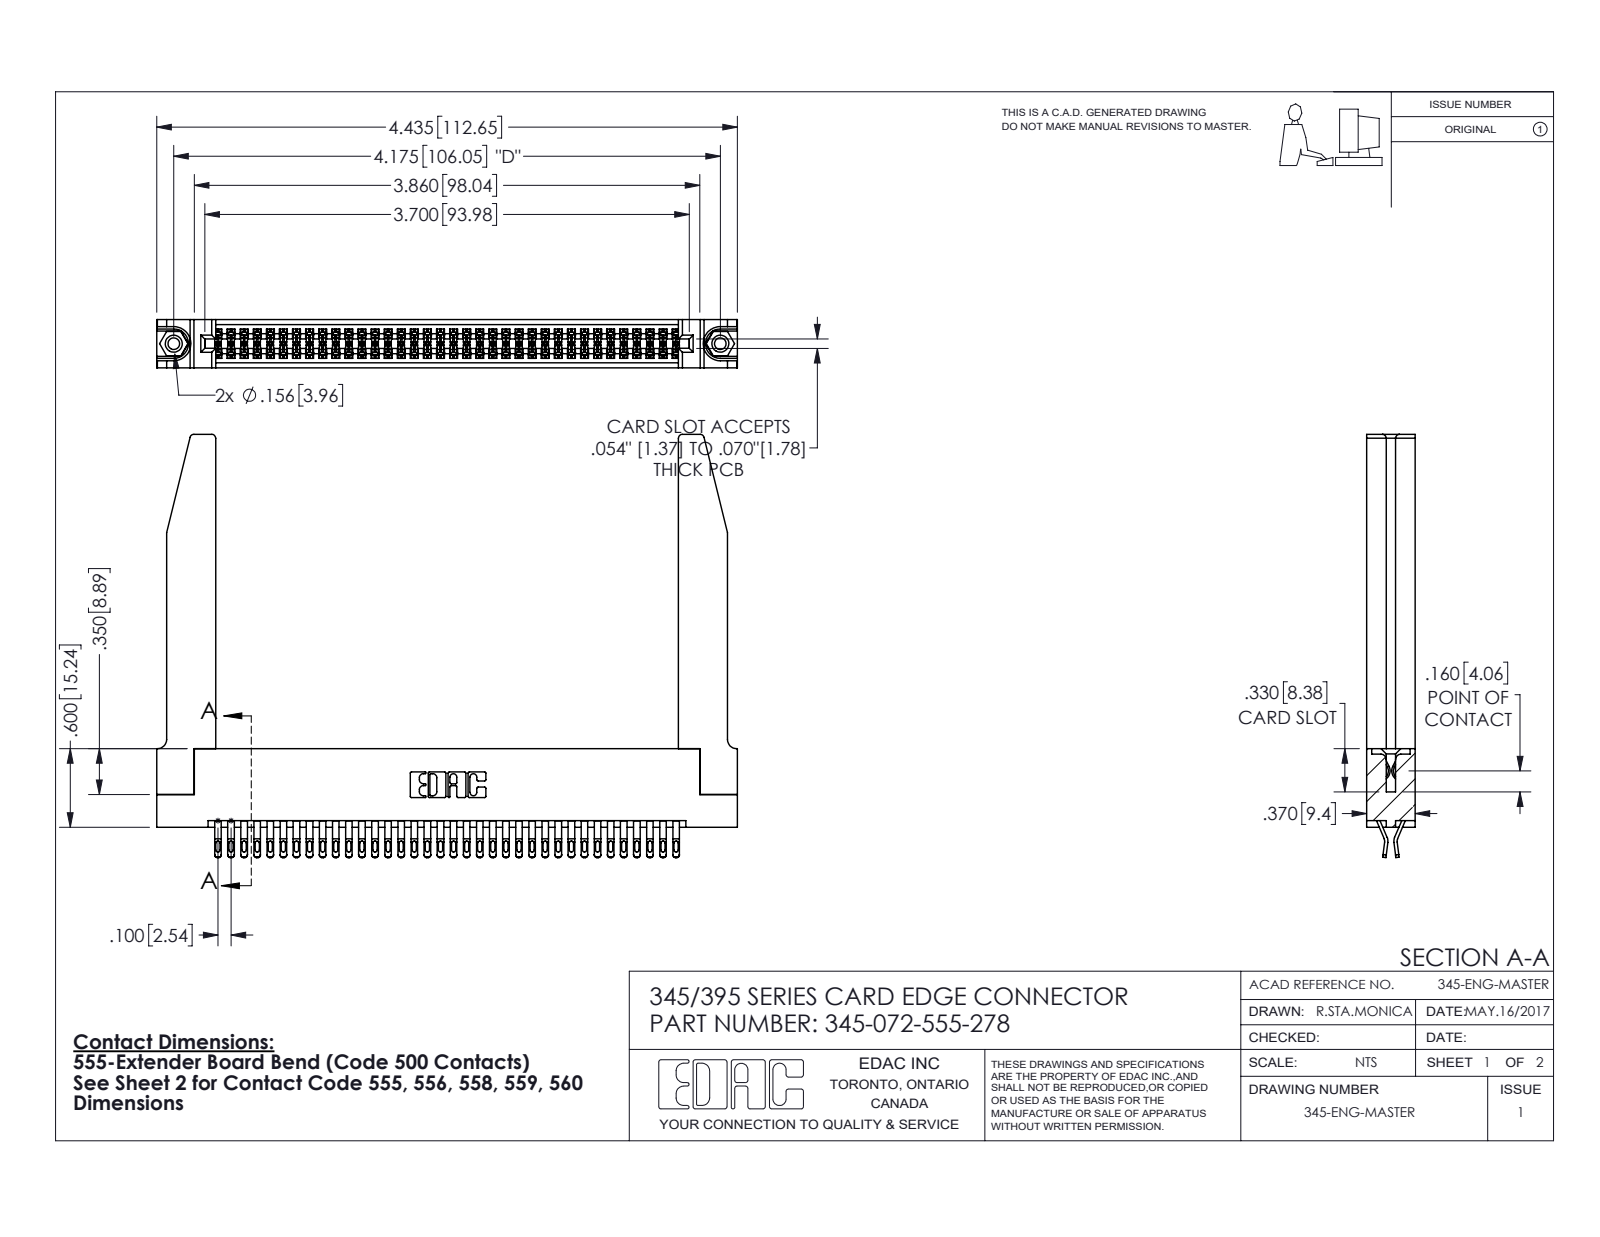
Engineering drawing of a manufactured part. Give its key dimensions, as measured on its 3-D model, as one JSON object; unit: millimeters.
{"part_name": "345-220-078_345-220-078; 345-292-001_555 Tail; 345 Part_Flush Mounting Lugs - 0.156 Dia-TH; 345-072-555-278 (+1 more)", "step_written_by": "SolidWorks 2016 (CONFIG_CONTROL_DESIGN)", "units": "millimeters", "bodies": {"solids": 77, "faces": 4392, "planar": 2454, "cylindrical": 1886, "other": 52}, "overall_size": [112.7, 82.1, 9.4], "volume_mm3": 18860, "surface_area_mm2": 23850, "round_holes": [[2.3, 2], [3.2, 2], [4, 2], [1.6, 1]], "round_bosses_or_shafts": [[3.9, 2]], "partial_cylinders_radius": [[0.4, 180], [0.5, 144], [0.2, 108], [0.3, 22], [0.8, 8], [0.2, 6], [0.8, 6], [0.7, 3]], "face_to_face_distances": [9.4, 1.8, 7.6, 5.1, 0.6, 2.5, 6.9, 5.7, 3.8, 3.8], "hole_center_spacings": [6.9, 100.1, 106]}
